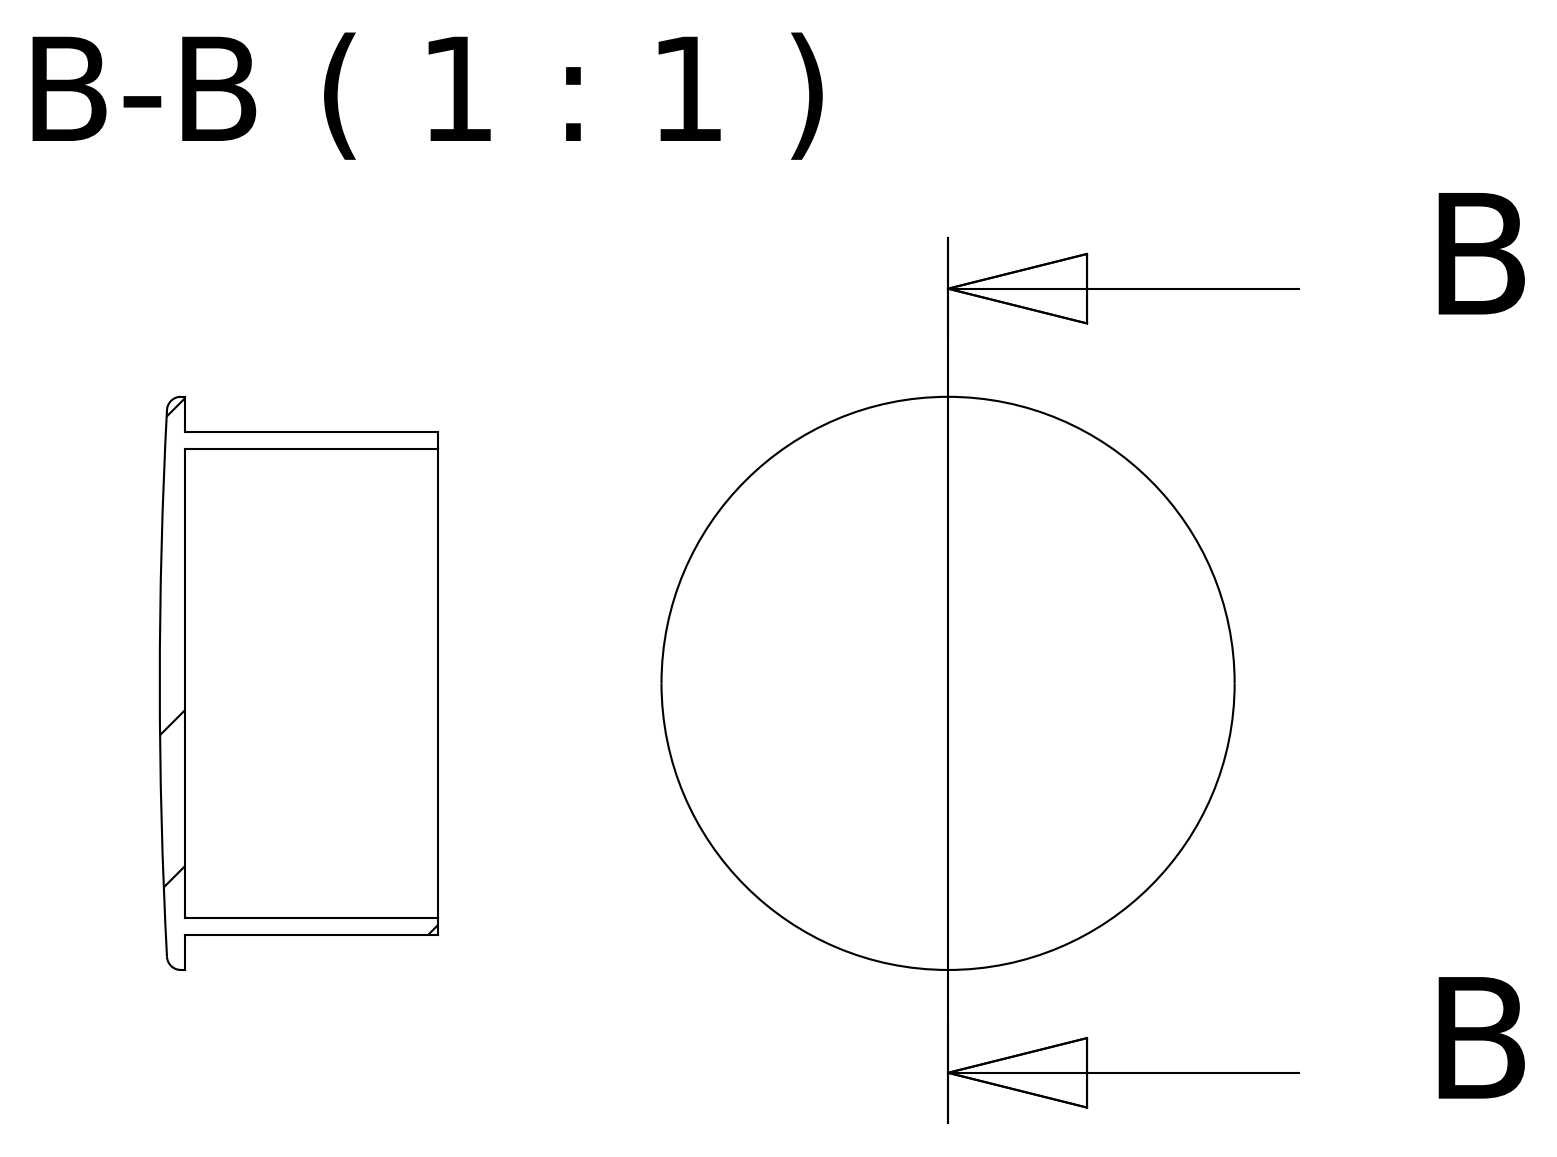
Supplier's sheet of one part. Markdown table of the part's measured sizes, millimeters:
| quantity | value |
| --- | --- |
| part name | 18.064.00G |
| STEP written by | Autodesk Inventor 2016 (AUTOMOTIVE_DESIGN) |
| units | millimeters |
| bodies | 1 solid, 8 faces (3 planar, 3 cylindrical, 2 other) |
| overall size | 16.5 × 16.5 × 8 |
| volume | 290 mm³ |
| surface area | 1 086 mm² |
| round holes (diameter × count) | 13.5 × 1 |
| round bosses / shafts (diameter × count) | 16.5 × 1, 14.5 × 1 |
| main face-to-face distances | 7.27 |
